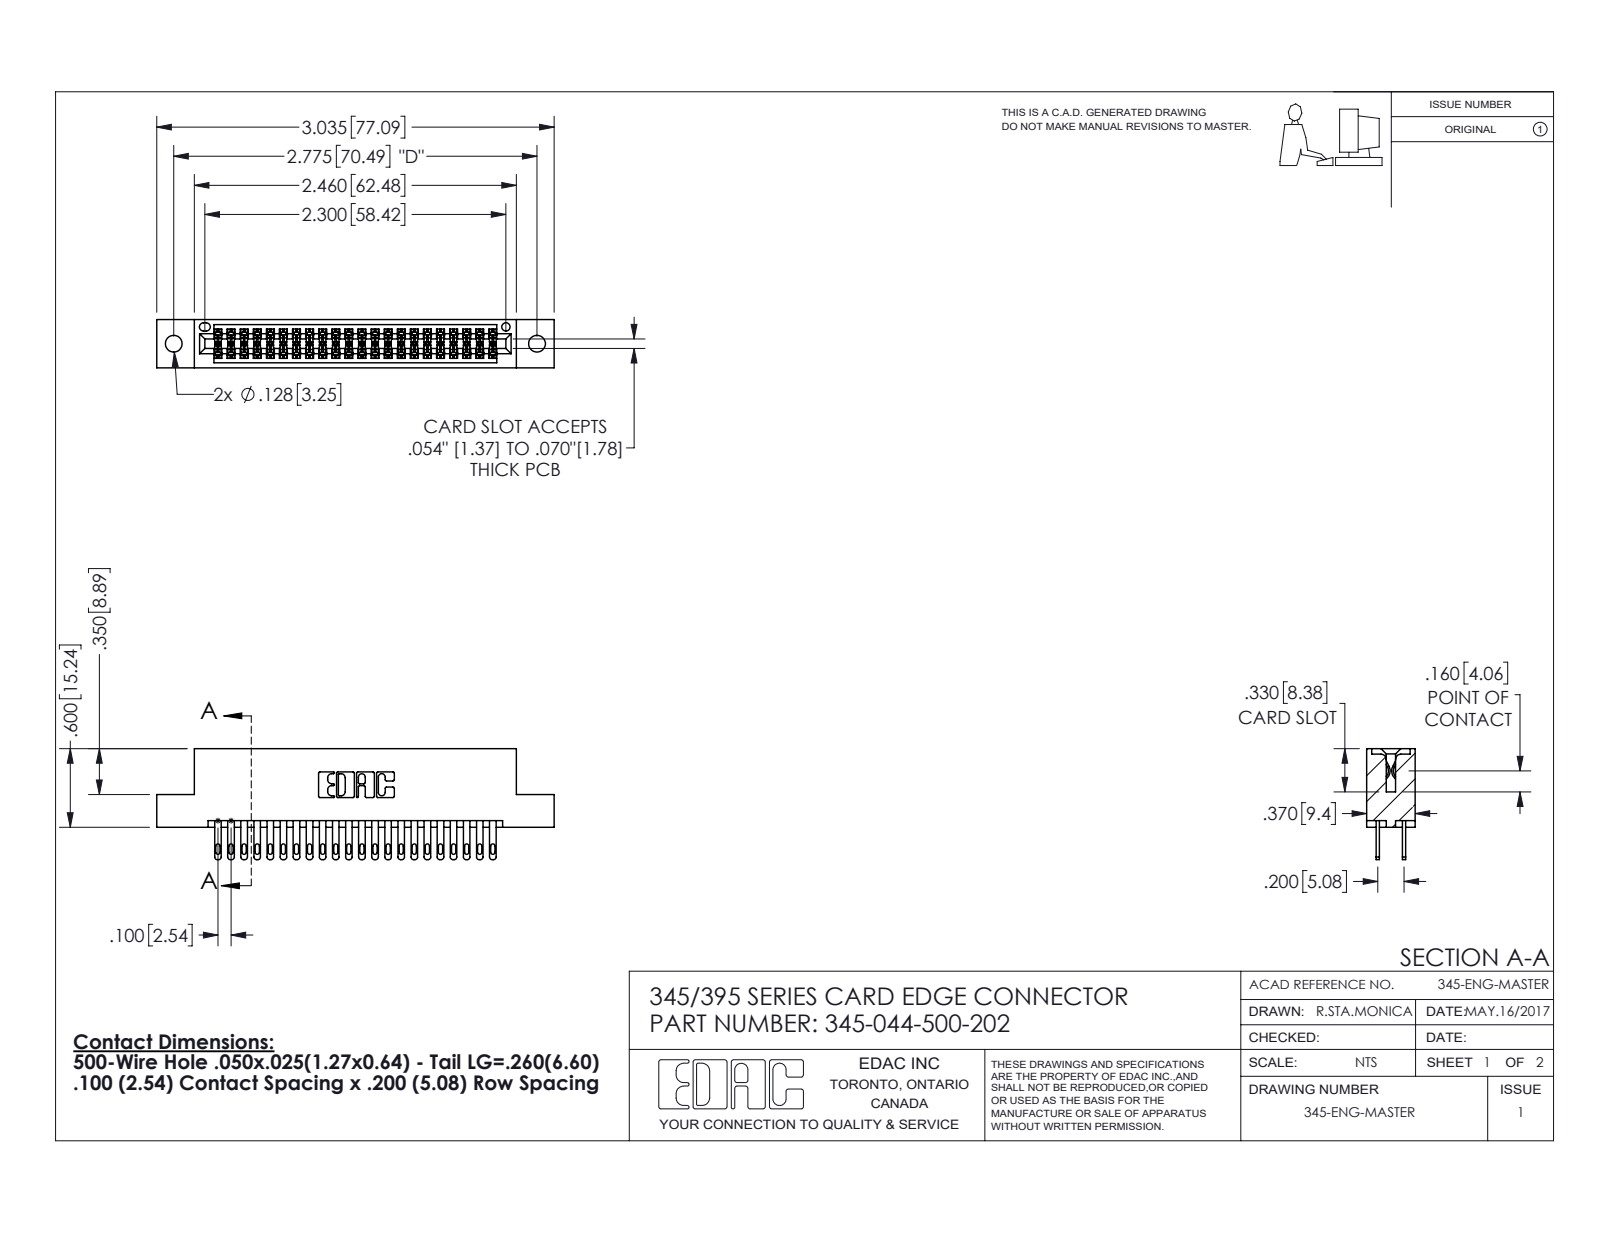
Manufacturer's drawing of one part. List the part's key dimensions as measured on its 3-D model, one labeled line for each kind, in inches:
Part name (STEP PRODUCT): 345-292-001_345-293-100; 345-044-500-202; 345 Part_Flush Mounting Lugs - 0.128 Dia
STEP written by: SolidWorks 2016 (CONFIG_CONTROL_DESIGN)
Units: inches
Bodies: 45 solids, 2150 faces (1268 planar, 882 cylindrical, 0 other)
Overall size (bounding box): 3.035 × 0.847 × 0.37
Volume: 0.452 in³ · Surface area: 16.63 in²
Round holes (diameter × count): ⌀0.128 ×2, ⌀0.064 ×1
Partial cylindrical surfaces — rounded edges, fillets, slot ends (radius × count): R0.006 ×66, R0.016 ×44, R0.02 ×44, R0.01 ×22, R0.007 ×6, R0.031 ×6, R0.026 ×3, R0.014 ×2
Main face-to-face distances: 0.298, 0.072, 0.2, 0.098, 0.272, 0.025, 0.37, 0.225, 0.175, 0.149
Hole centre spacings: 0.27, 2.541, 2.775
